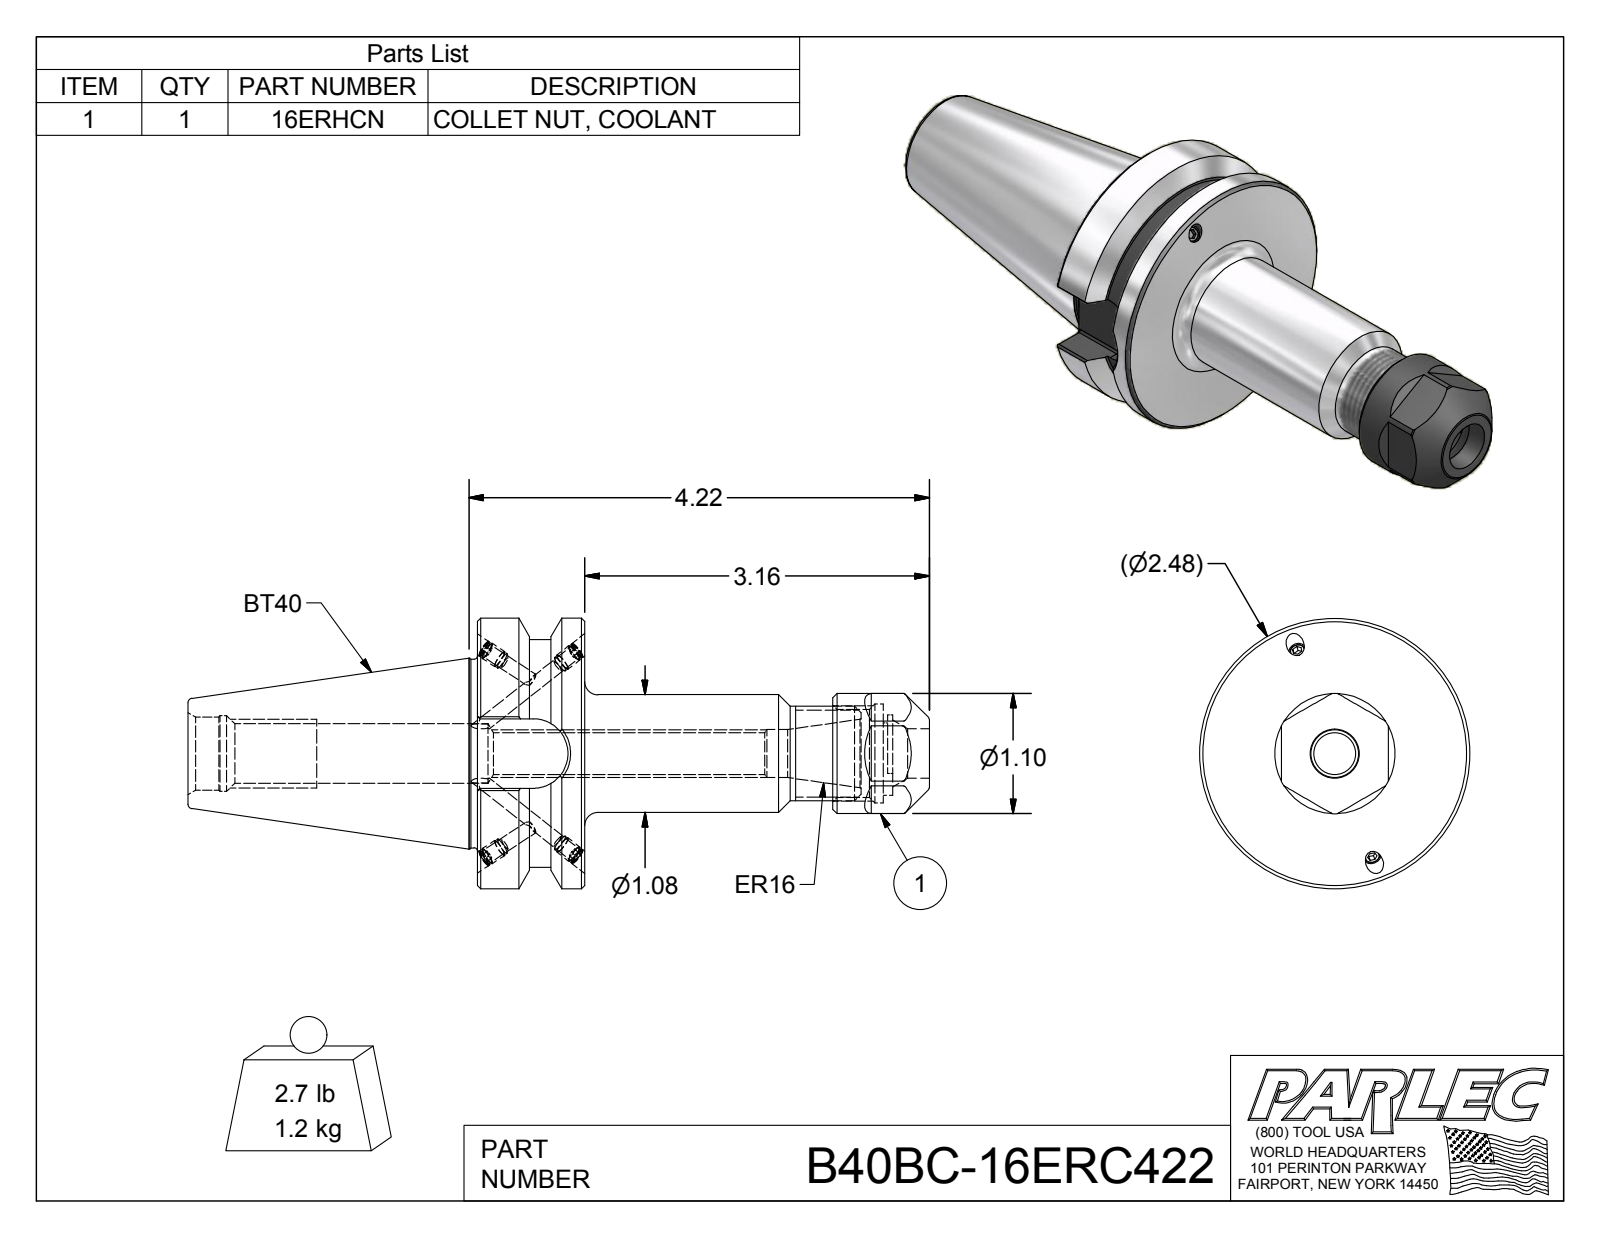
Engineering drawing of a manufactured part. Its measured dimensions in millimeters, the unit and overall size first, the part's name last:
Units: millimetres
Overall size (bounding box): 172.6 × 63 × 63
Round holes (diameter × count): ⌀3.3 ×4, ⌀4.1 ×4, ⌀9.7 ×1, ⌀11.2 ×1, ⌀11.5 ×1, ⌀13.8 ×1, ⌀16.8 ×1, ⌀17 ×1, ⌀17.6 ×1, ⌀20.5 ×1, ⌀23 ×1
Round bosses / shafts (diameter × count): ⌀4.2 ×4, ⌀4 ×4, ⌀63 ×1, ⌀53 ×1, ⌀43.9 ×1, ⌀28 ×1, ⌀27.4 ×1, ⌀22 ×1
Partial cylindrical surfaces — rounded edges, fillets, slot ends (radius × count): R0.5 ×8, R8.1 ×1, R9 ×1
Main face-to-face distances: 25, 24.9, 45.2, 10.2, 35.1, 94.5, 69.5, 67.4, 92.4, 161.9
Hole centre spacings: 1.3
Volume: 154 800 mm³ · Surface area: 34 410 mm²
Bodies: 6 solids, 186 faces (84 planar, 49 cylindrical, 53 other)
Part name (STEP PRODUCT): B40BC-16ERC422; B40BCB-16ER4-1; 029-965; 16ERHCN
STEP written by: Autodesk Inventor 2012 (AUTOMOTIVE_DESIGN)
